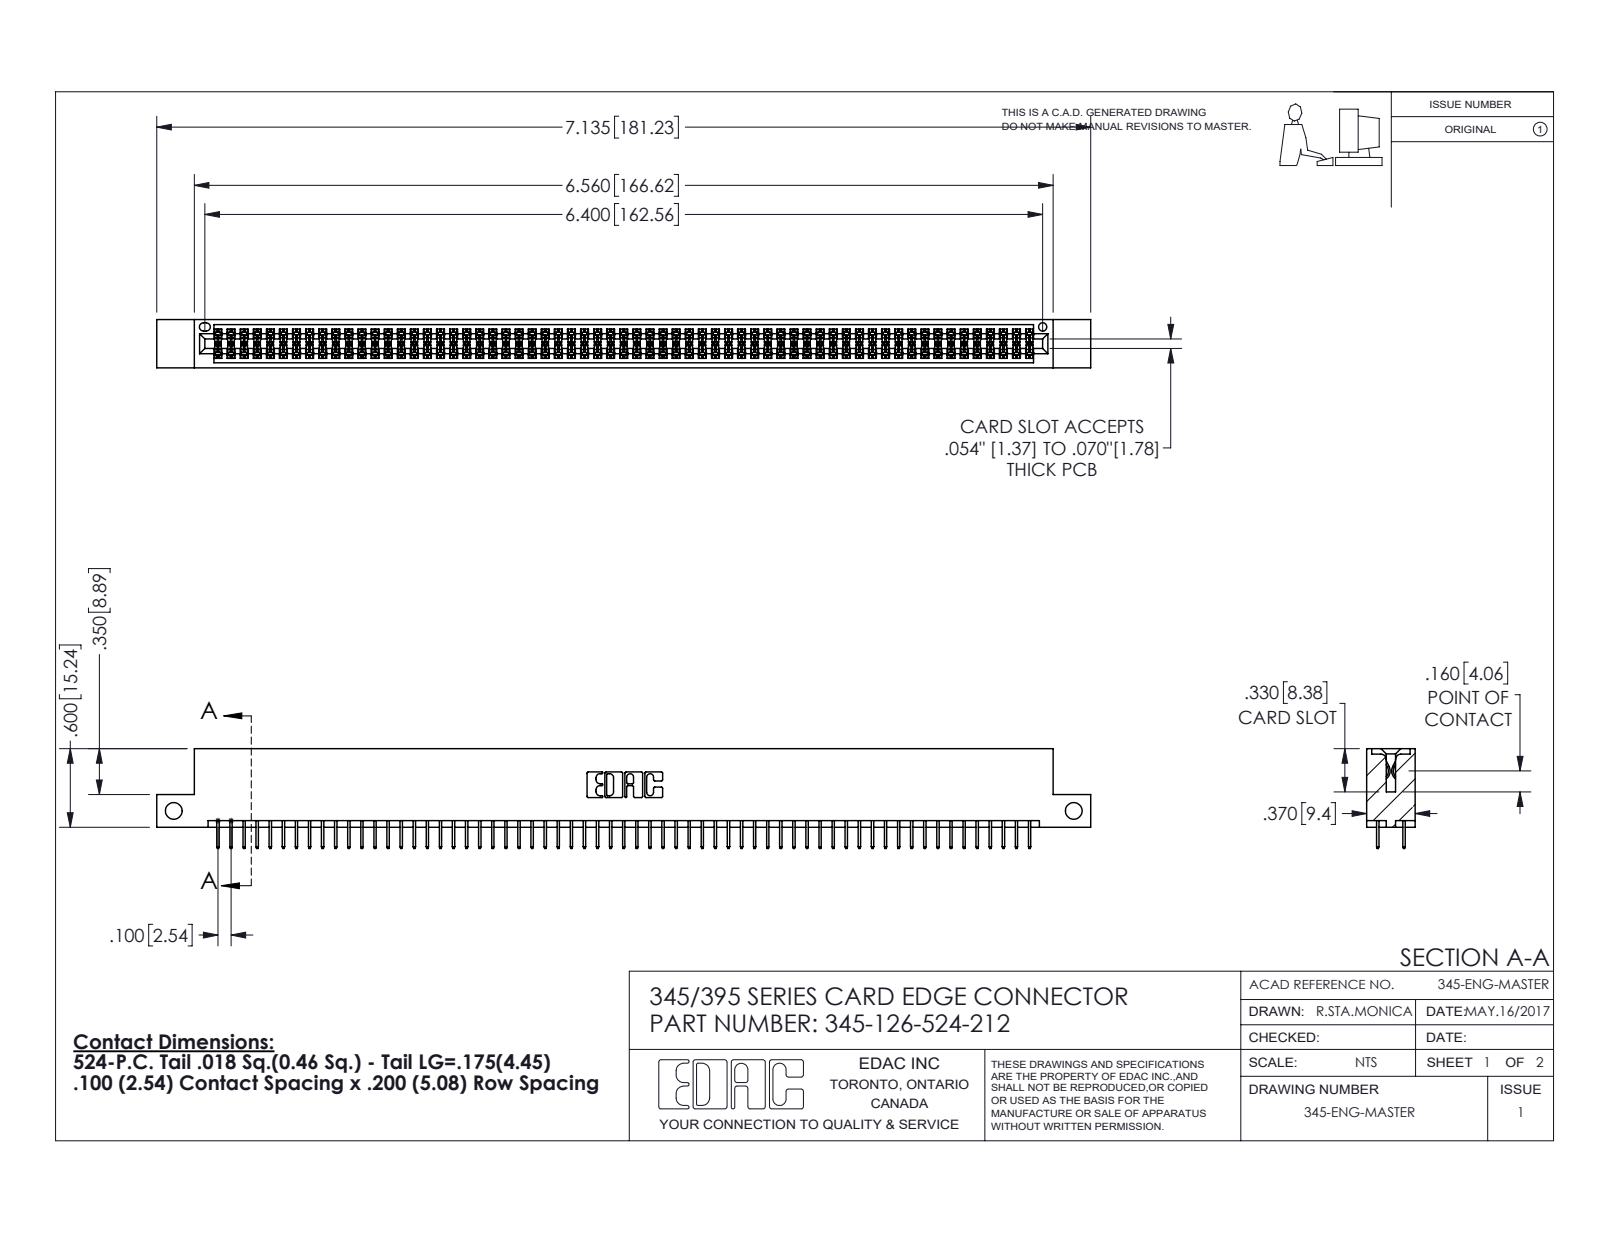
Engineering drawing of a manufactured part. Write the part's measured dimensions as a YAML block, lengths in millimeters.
part_name: "345 Part_Flush Mounting Lugs - Side Mount; 345-126-524-212; 345-292-001_345-293-124"
step_written_by: "SolidWorks 2016 (CONFIG_CONTROL_DESIGN)"
units: millimeters
bodies: {solids: 127, faces: 6930, planar: 4994, cylindrical: 1936, other: 0}
overall_size: [181.2, 19.4, 9.4]
volume: 17520
surface_area: 25670
round_holes:
  - {diameter: 3.3, count: 2}
  - {diameter: 1.6, count: 1}
partial_cylinders:
  - {radius: 0.2, count: 189}
  - {radius: 0.3, count: 22}
  - {radius: 0.2, count: 6}
  - {radius: 0.8, count: 6}
  - {radius: 0.7, count: 3}
  - {radius: 0.4, count: 2}
  - {radius: 0.5, count: 2}
  - {radius: 0.6, count: 2}
face_to_face_distances: [1.8, 7.6, 5.1, 9.4, 2.5, 6.9, 0.6, 5.7, 1.8, 4.4]
hole_center_spacings: [174.6]
